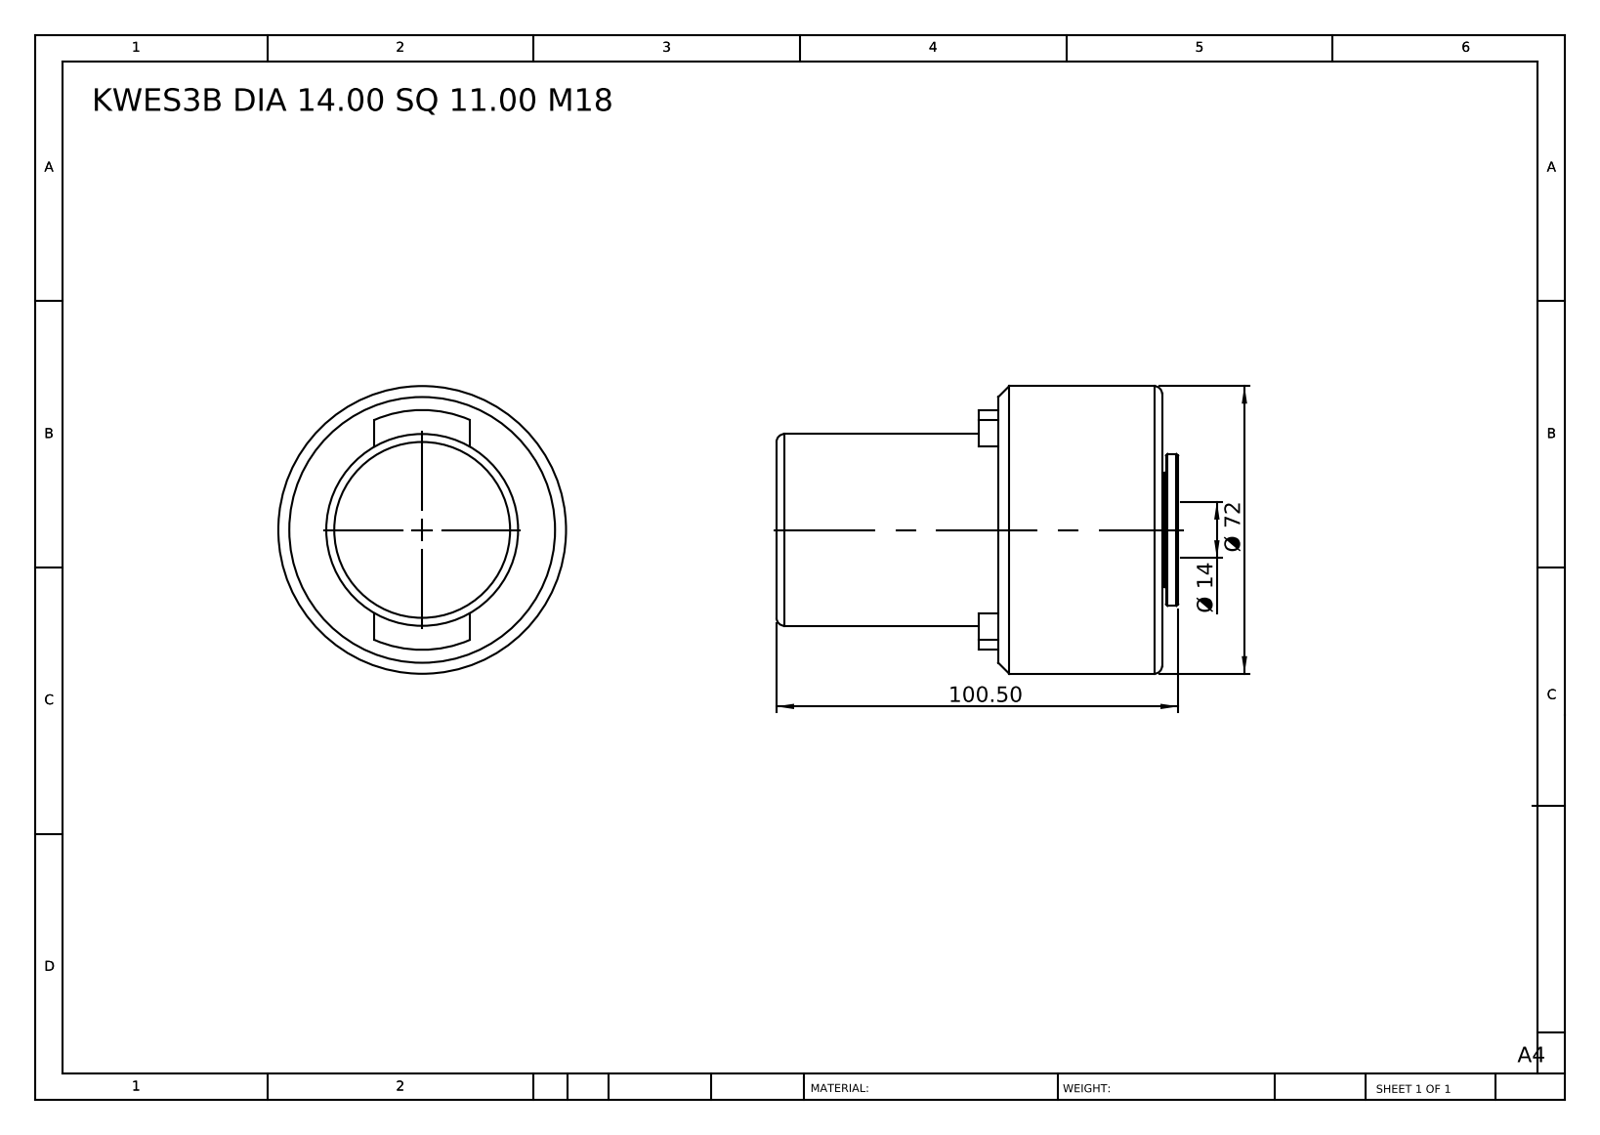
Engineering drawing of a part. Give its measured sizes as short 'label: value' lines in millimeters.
name: KWES3B DIA 14.00 SQ 11.00 11-16'''''''' UNC
written by: SolidWorks 2014 (CONFIG_CONTROL_DESIGN)
unit: mm
bodies: 1 solid, 39 faces (12 planar, 13 cylindrical, 14 other)
size: 100.5 × 72 × 72
volume: 265 559 mm³; area: 28 330 mm²
holes: 1× ⌀14
bosses: 1× ⌀72, 1× ⌀48, 1× ⌀38, 1× ⌀28.5
rounds: 1× R30
face distances: 96.5, 55.5, 41, 100.5, 45, 4, 5, 97.5, 42, 1
